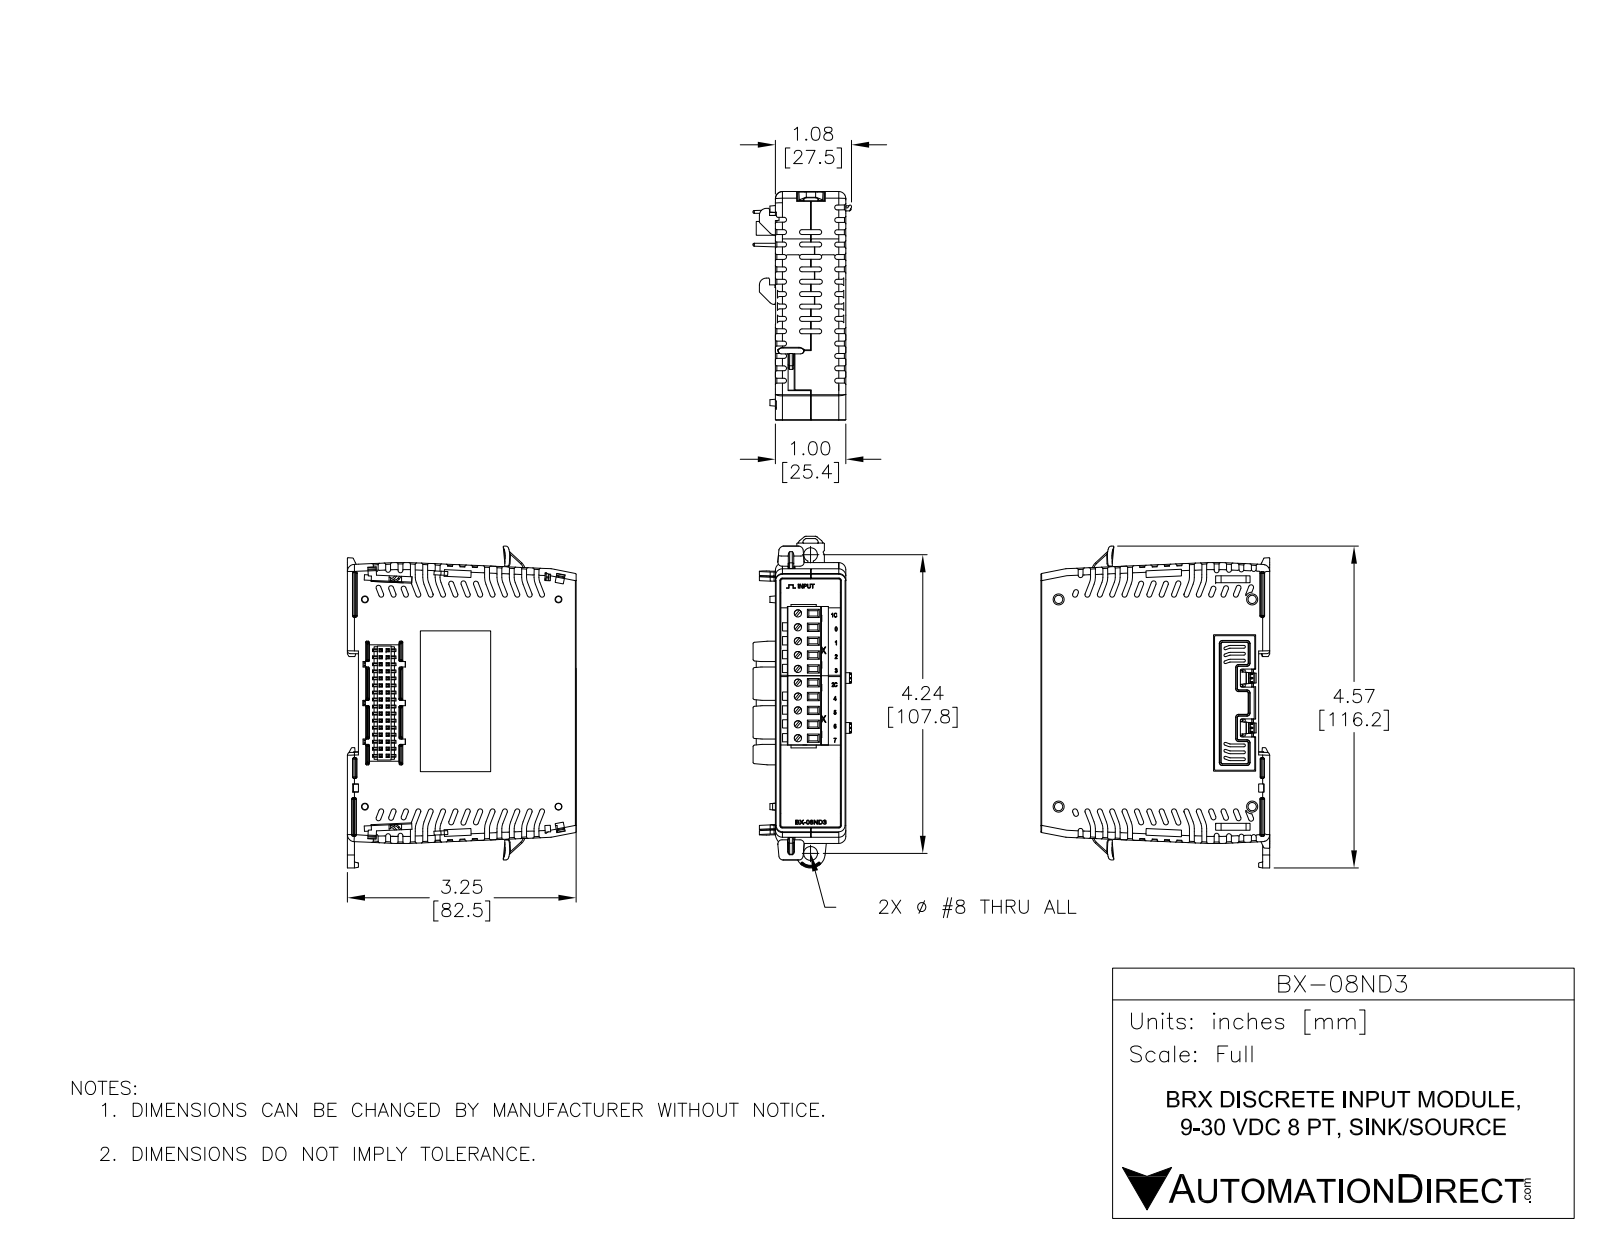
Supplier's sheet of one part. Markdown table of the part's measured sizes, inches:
| quantity | value |
| --- | --- |
| part name | BX-08ND3 |
| STEP written by | SolidWorks 2017 (AUTOMOTIVE_DESIGN) |
| units | inches |
| bodies | 22 solids, 3587 faces (2546 planar, 563 cylindrical, 478 other) |
| overall size | 4.586 × 3.311 × 1.402 |
| volume | 11.59 in³ |
| surface area | 72.76 in² |
| round holes (diameter × count) | 0.047 × 2, 0.065 × 2, 0.118 × 2, 0.118 × 2, 0.199 × 1 |
| round bosses / shafts (diameter × count) | 0.062 × 2, 0.059 × 2 |
| partial cylindrical surfaces (radius × count) | 0.005 × 102, 0.01 × 47, 0.02 × 34, 0.005 × 24, 0.008 × 21, 0.117 × 14, 0.039 × 13, 0.01 × 12 |
| main face-to-face distances | 1, 3.211, 3.22, 0.475, 0.1, 0.157, 3.053, 3.063, 0.787, 0.63 |
| hole center spacings | 0.1, 0.824, 0.919, 1.3, 2.093, 2.193, 2.585, 2.617 |
